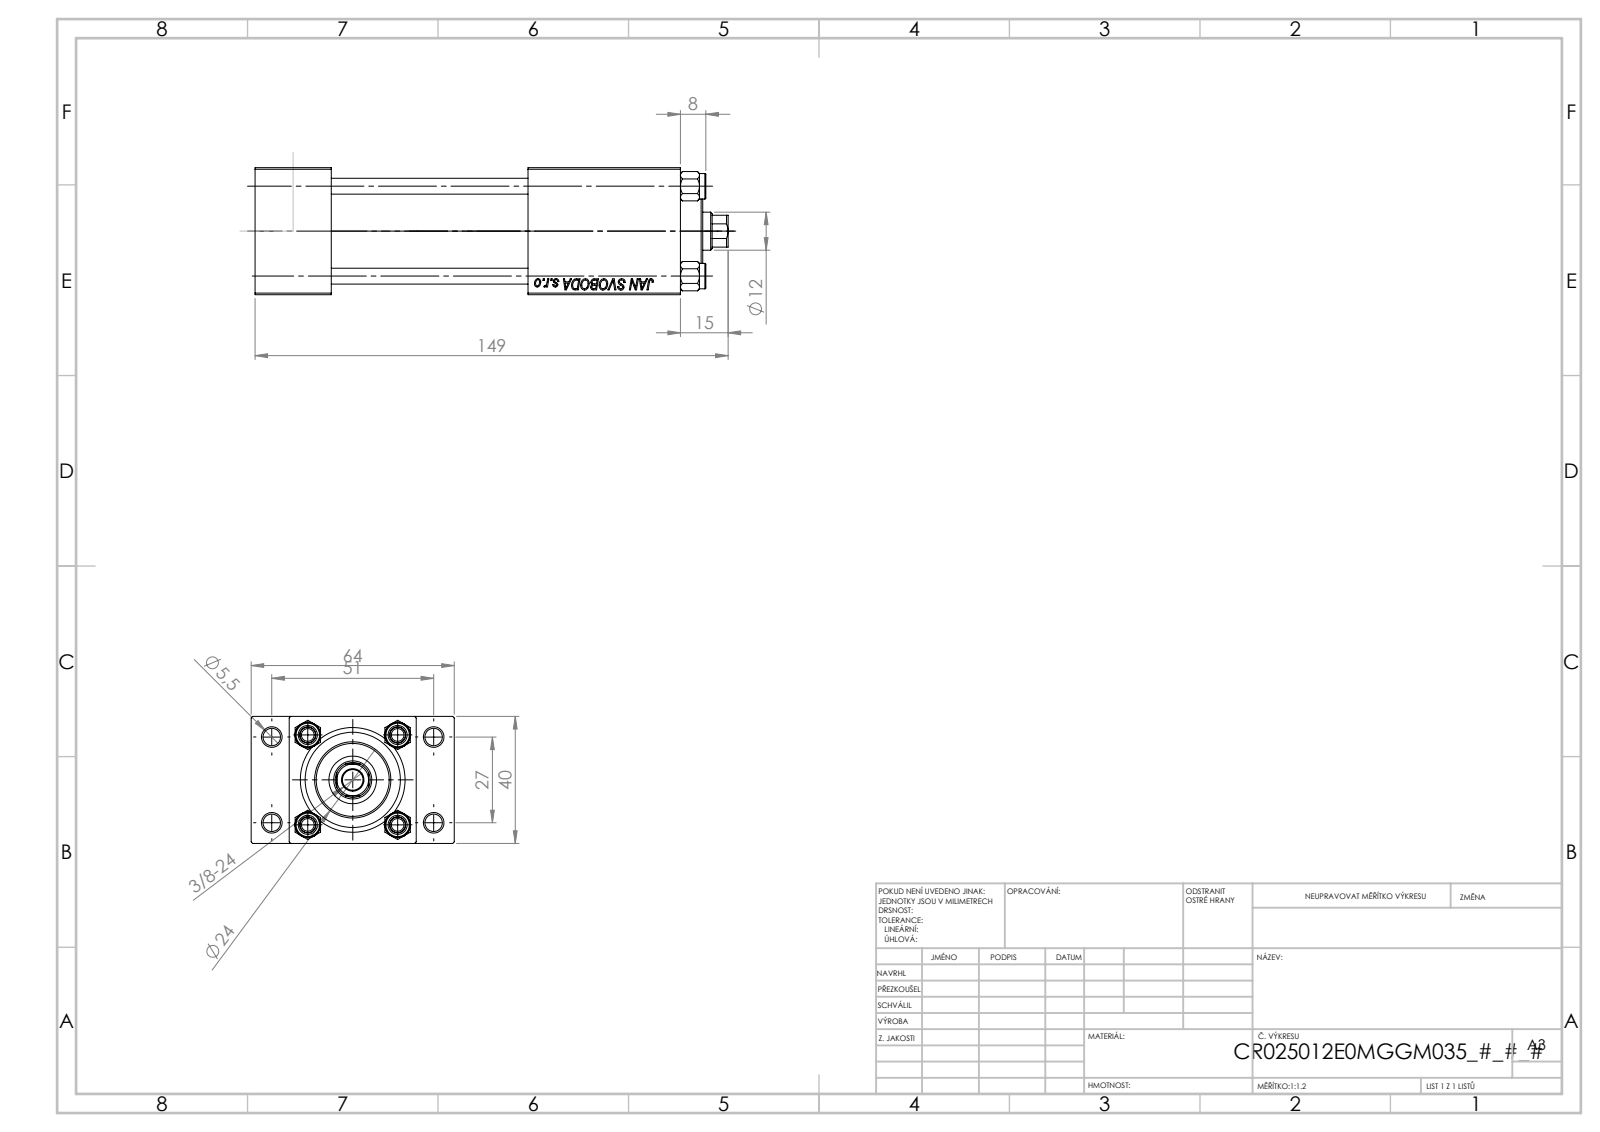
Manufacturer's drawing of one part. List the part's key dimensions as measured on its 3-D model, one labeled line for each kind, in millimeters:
Part name (STEP PRODUCT): V215CR_E_Body; V215CR_VCP_E; V215_VC_A; NUT_M5_E (+1 more)
STEP written by: SolidWorks 2019 (CONFIG_CONTROL_DESIGN)
Units: millimetres
Bodies: 11 solids, 1136 faces (497 planar, 87 cylindrical, 552 other)
Overall size (bounding box): 149 × 64 × 40
Volume: 170 748 mm³ · Surface area: 66 252 mm²
Round holes (diameter × count): ⌀5 ×4, ⌀5.5 ×4, ⌀20 ×3, ⌀7 ×2, ⌀13.16 ×2, ⌀6.5 ×1, ⌀12 ×1, ⌀15 ×1, ⌀25 ×1, ⌀30 ×1
Round bosses / shafts (diameter × count): ⌀8 ×4, ⌀31 ×1, ⌀24 ×1
Partial cylindrical surfaces — rounded edges, fillets, slot ends (radius × count): R5.5 ×1
Main face-to-face distances: 40, 24, 12, 52, 134, 110, 105.3, 81.3, 28.7, 64
Hole centre spacings: 11.37, 20.01, 28.3, 28.85, 29.89, 39.66, 48.34, 27
